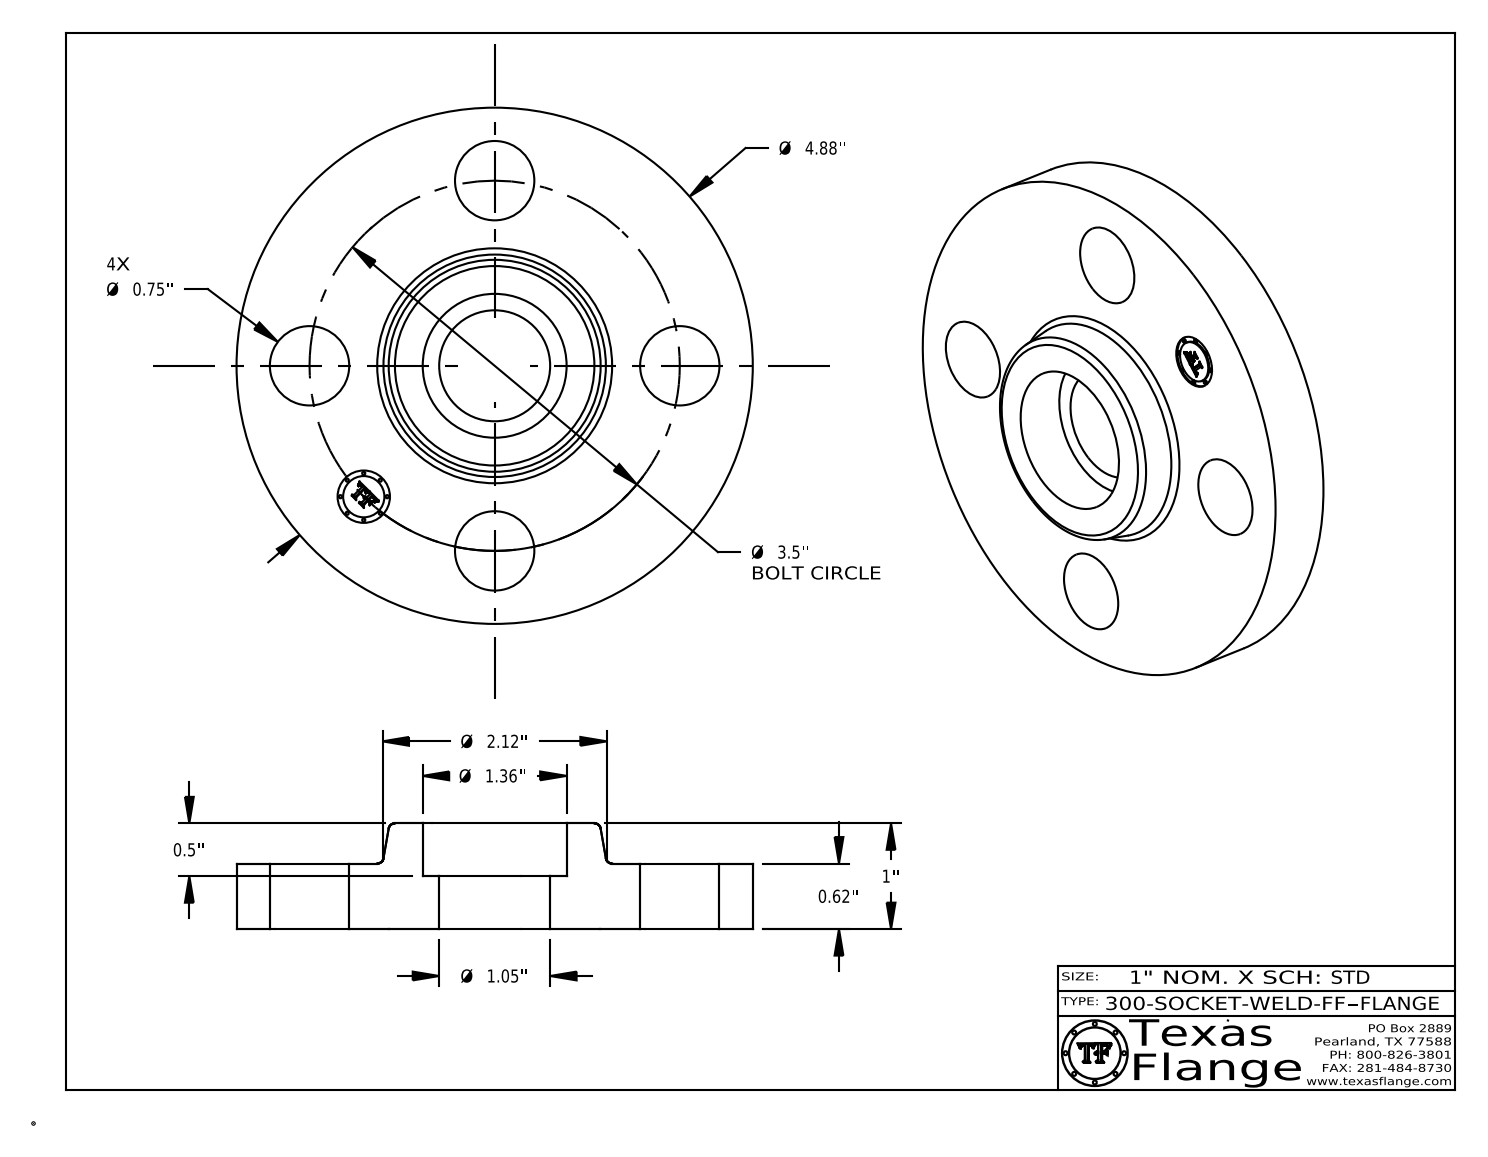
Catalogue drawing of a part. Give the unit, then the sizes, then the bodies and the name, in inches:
Units: inches
Overall size (bounding box): 4.88 × 4.88 × 1
Round holes (diameter × count): ⌀0.75 ×4, ⌀0.495 ×1, ⌀1.049 ×1, ⌀1.36 ×1
Round bosses / shafts (diameter × count): ⌀0.03 ×8, ⌀4.88 ×1, ⌀0.39 ×1
Main face-to-face distances: 0.62, 1, 0.38, 0.5, 0.12, 0.105, 0.015, 0.605, 0.395, 0.148
Hole centre spacings: 1.75, 2.475, 1.339, 3.233, 3.5
Volume: 10.6 in³ · Surface area: 53.21 in²
Bodies: 1 solid, 410 faces (370 planar, 34 cylindrical, 6 other)
Part name (STEP PRODUCT): 300-SOCKET-WELD-FF
STEP written by: CATIA V5 STEP AP214 (AUTOMOTIVE_DESIGN)
